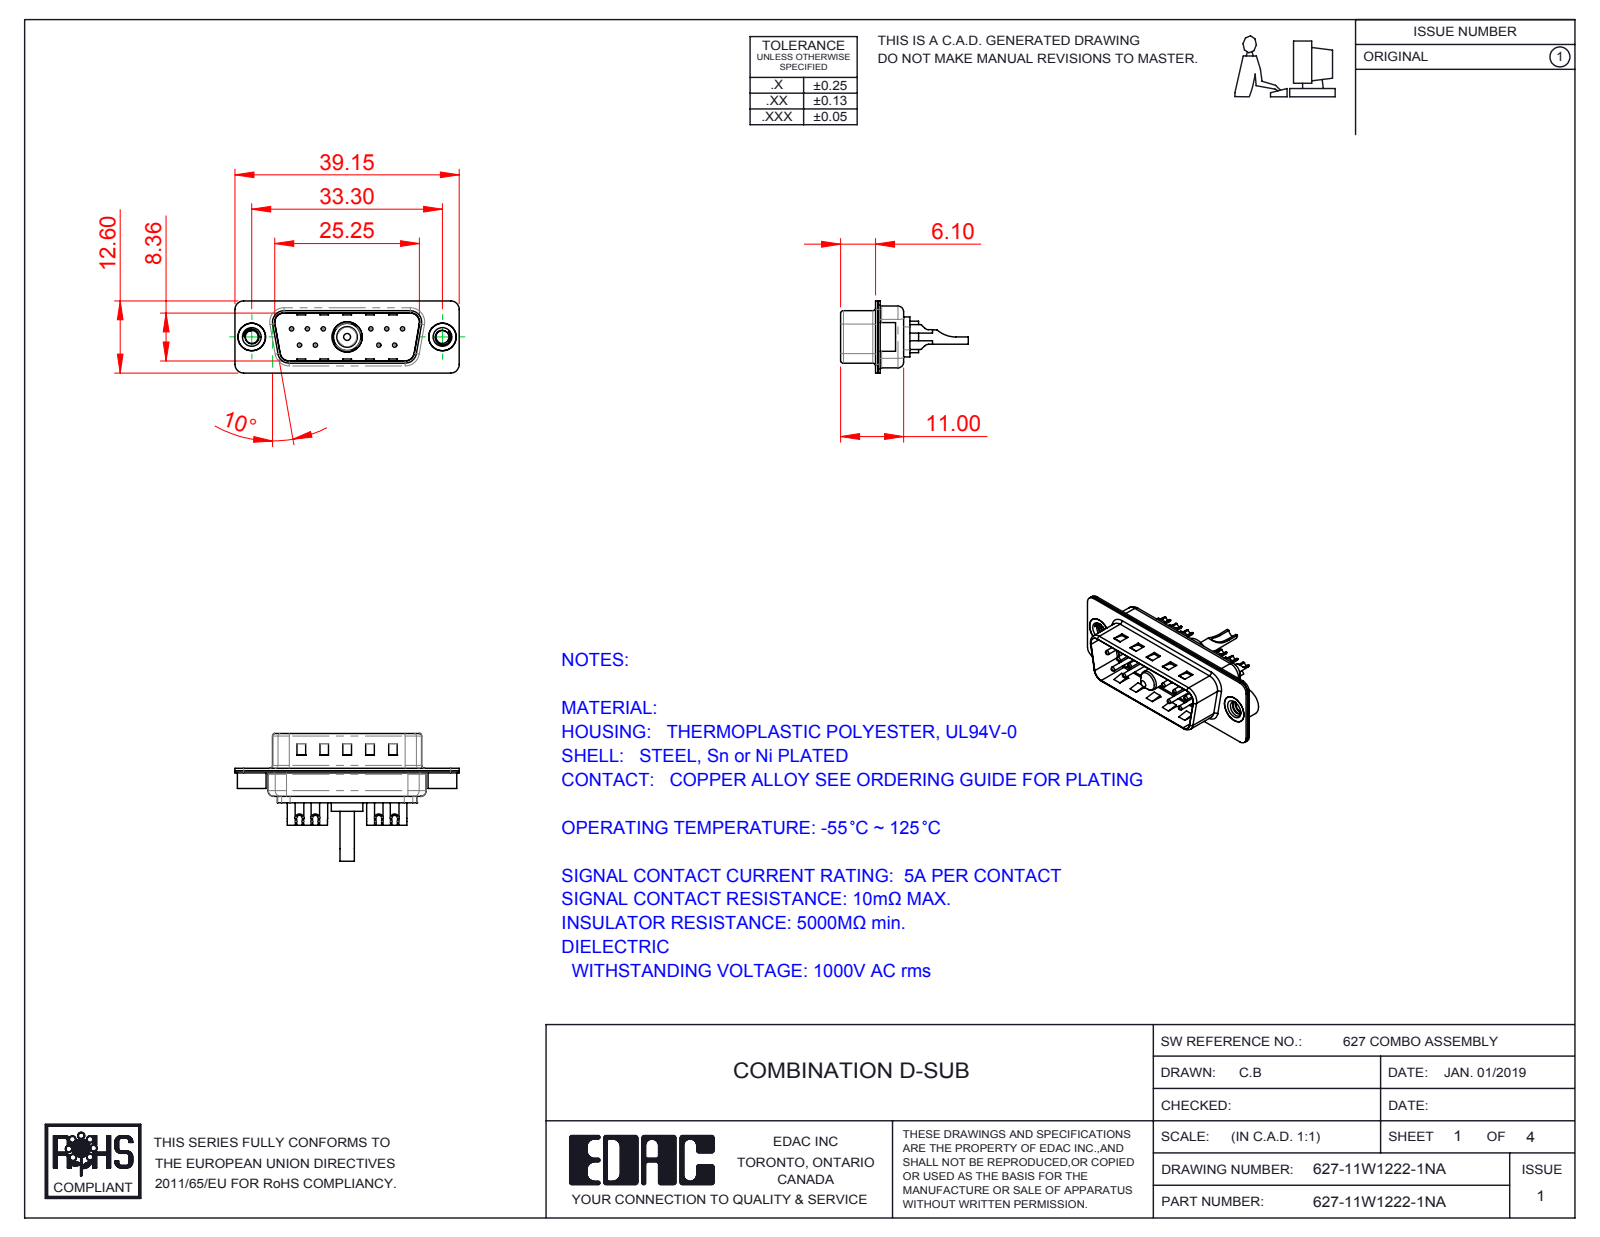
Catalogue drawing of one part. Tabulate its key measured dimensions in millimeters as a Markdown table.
| quantity | value |
| --- | --- |
| part name | 627-11W1222-1NA; 627Combo Threaded Rivet_2; 627Combo Shell Rear_15 Contacts; 627Combo Shell Front_15 Contacts (+5 more) |
| STEP written by | SolidWorks 2016 (CONFIG_CONTROL_DESIGN) |
| units | millimeters |
| bodies | 17 solids, 767 faces (250 planar, 320 cylindrical, 197 other) |
| overall size | 39.15 × 22.3 × 12.6 |
| volume | 1 925 mm³ |
| surface area | 4 916 mm² |
| round holes (diameter × count) | 0.75 × 10, 1 × 10, 1.6 × 10, 2 × 10, 2.26 × 2, 4 × 2, 4.8 × 2, 1.7 × 1, 4.85 × 1, 5.3 × 1 |
| round bosses / shafts (diameter × count) | 1.5 × 10, 5 × 2, 4.9 × 2, 5.5 × 1, 5.2 × 1, 4.75 × 1, 3.75 × 1, 3.6 × 1 |
| partial cylindrical surfaces (radius × count) | 1.5 × 20, 2 × 12, 1 × 9, 0.5 × 8, 1.6 × 8, 0.25 × 4, 0.6 × 4, 0.65 × 4 |
| main face-to-face distances | 0.4, 0.82, 9.58, 8.76, 0.8, 1.5, 5.6, 1.4, 5.2, 6 |
| hole center spacings | 3.16, 2.77, 13.85, 11.08, 16.62, 5.03, 5.04, 5.54 |
